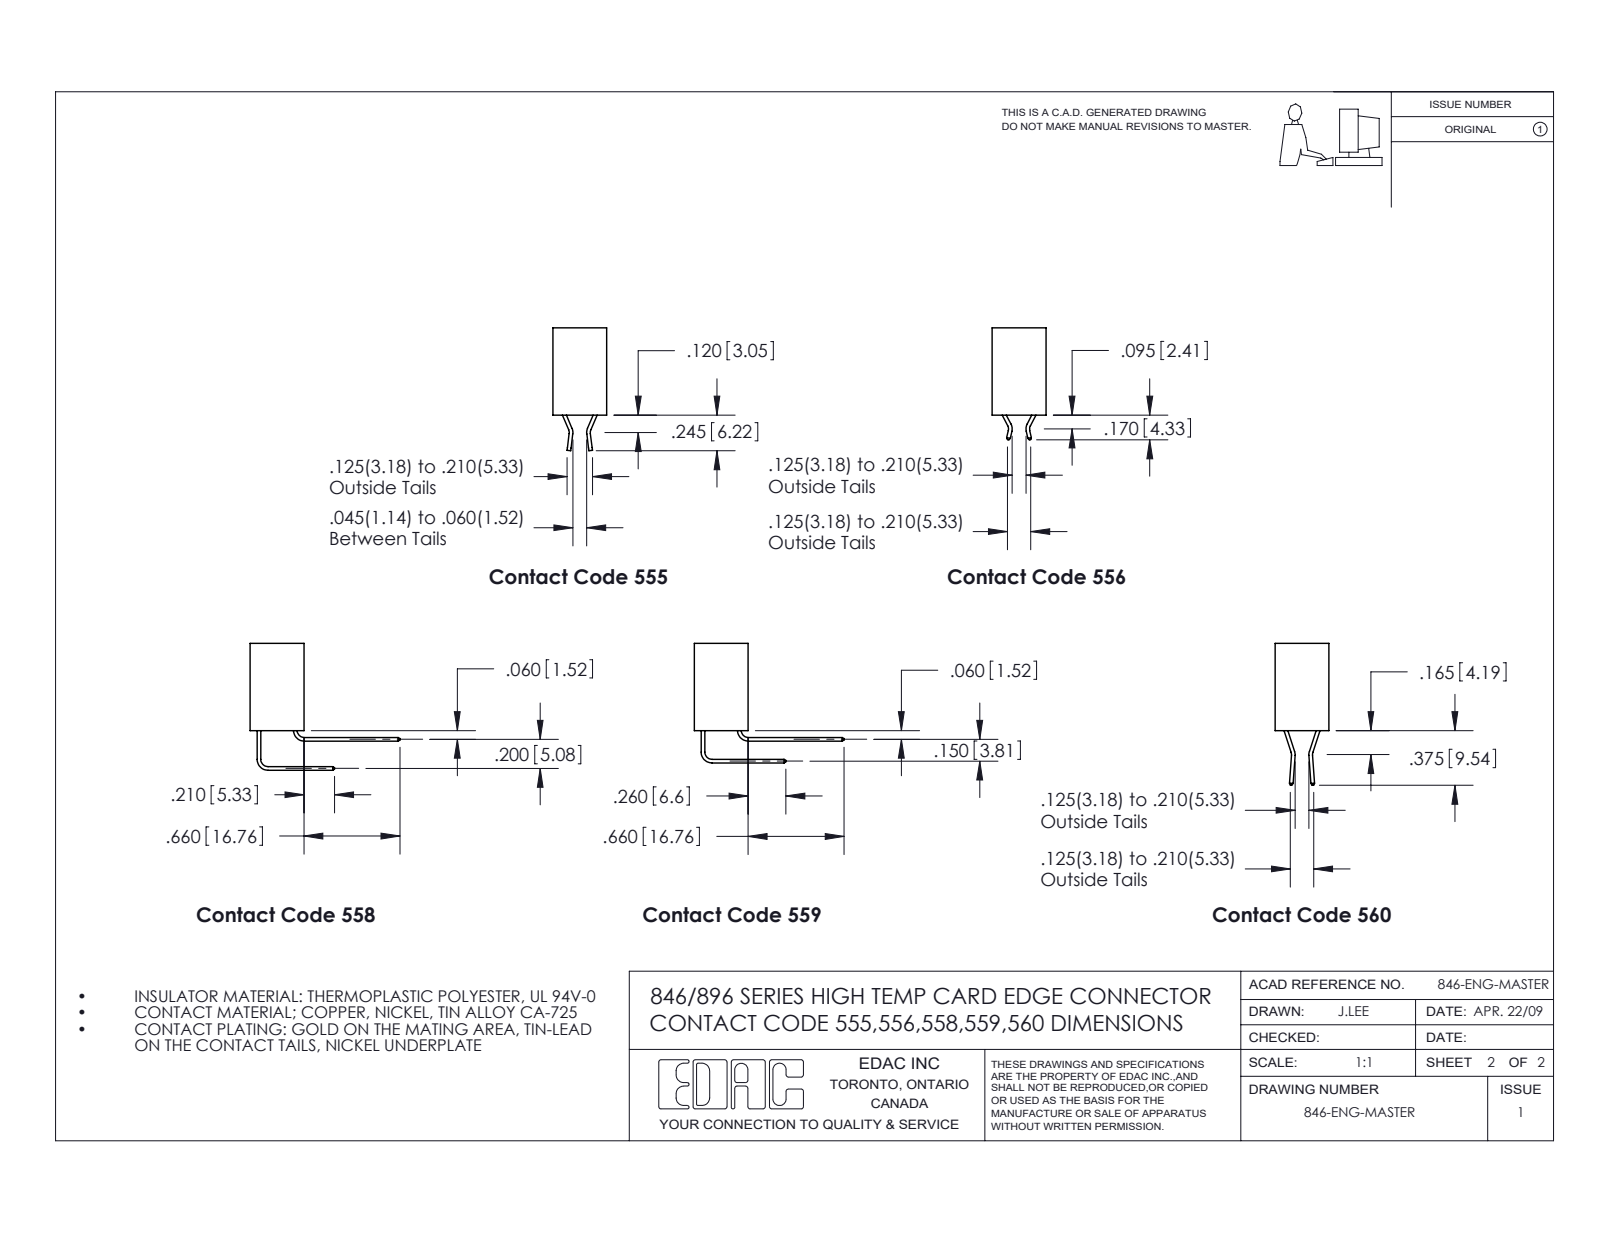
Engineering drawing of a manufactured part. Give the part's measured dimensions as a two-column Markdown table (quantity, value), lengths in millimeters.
| quantity | value |
| --- | --- |
| part name | 346 Part_Flush Mounting Lugs - 0.128 Dia; 345-292-001_345-293-141; 396-006-541-102 |
| STEP written by | SolidWorks 2016 (CONFIG_CONTROL_DESIGN) |
| units | millimeters |
| bodies | 7 solids, 470 faces (316 planar, 154 cylindrical, 0 other) |
| overall size | 39.6 × 34.3 × 9.4 |
| volume | 3 520 mm³ |
| surface area | 3 868 mm² |
| round holes (diameter × count) | 3.3 × 2, 1.6 × 1 |
| partial cylindrical surfaces (radius × count) | 0.3 × 22, 0.2 × 12, 0.3 × 12, 0.2 × 6, 0.8 × 6, 0.7 × 3, 0.8 × 2, 1 × 2 |
| main face-to-face distances | 6.4, 9.4, 1.2, 8.2, 1.8, 7.6, 0.6, 3.8, 5.6, 2.5 |
| hole center spacings | 6.2, 27.7, 32.9 |
